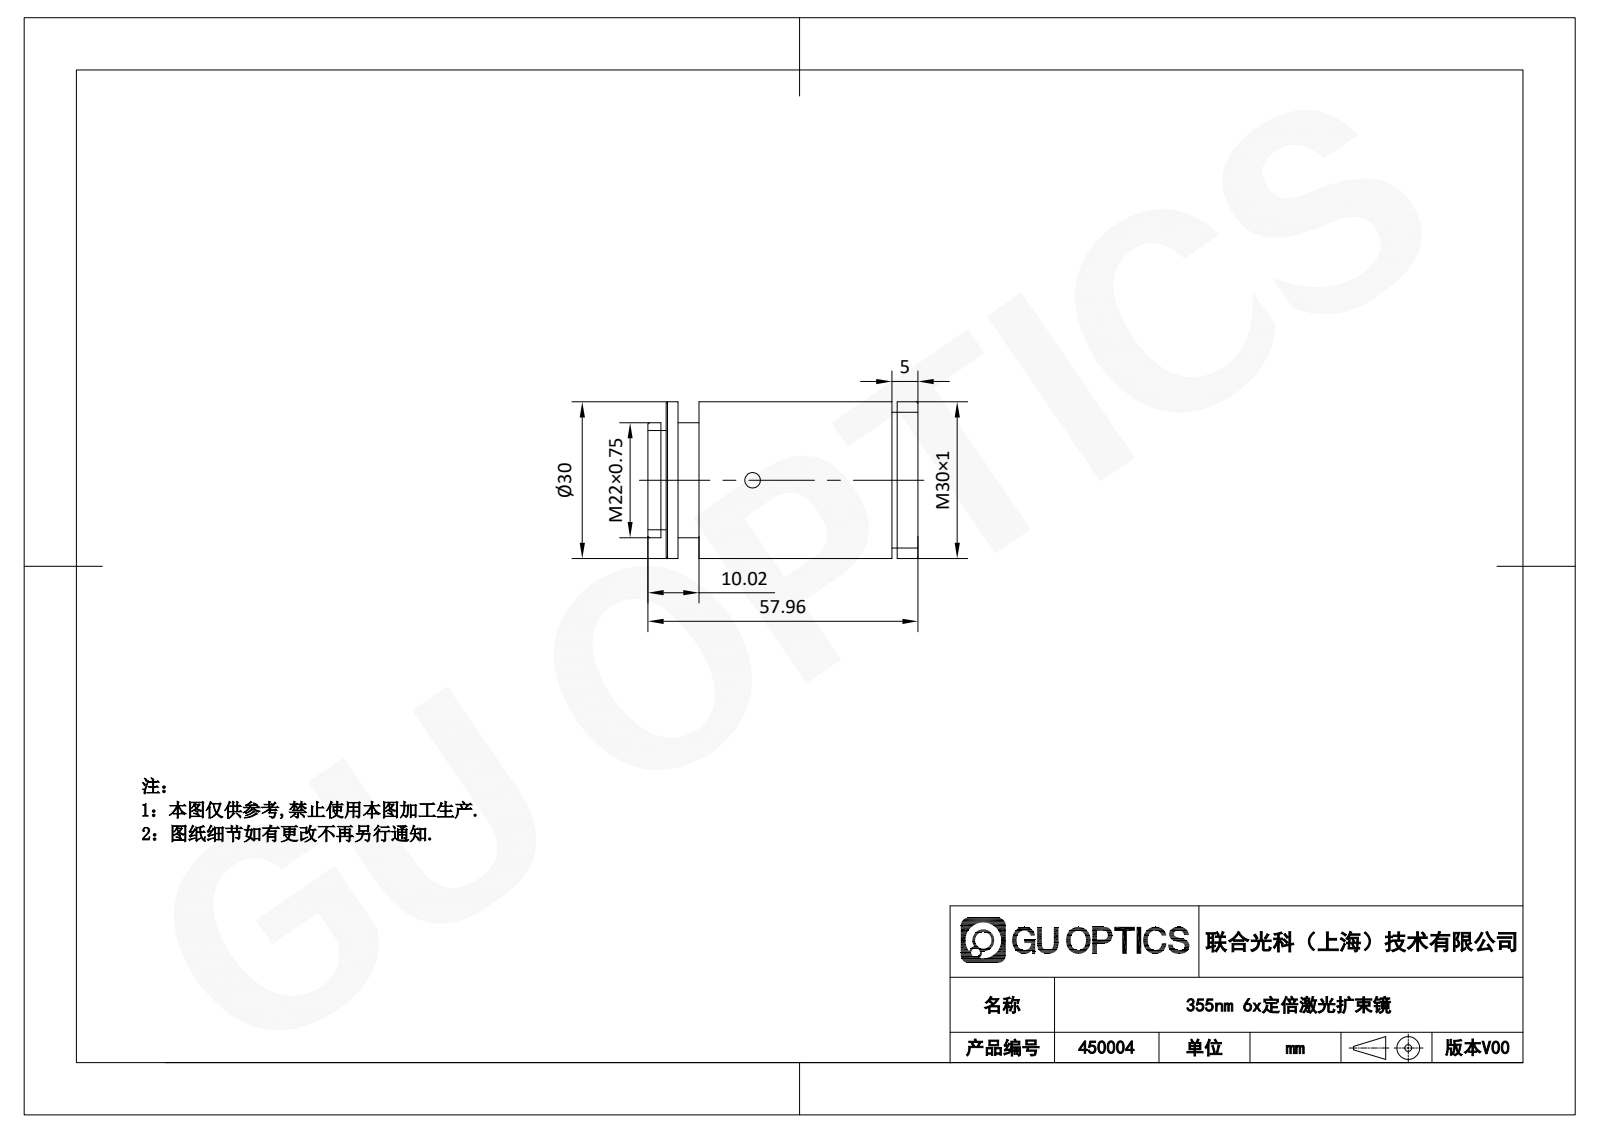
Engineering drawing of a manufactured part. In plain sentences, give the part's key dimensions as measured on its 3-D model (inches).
The part is named "450004". Its 3-D file was written by "SolidWorks 2020 (AUTOMOTIVE_DESIGN)". It is 1 solid with 43 faces: 11 planar, 22 cylindrical and 10 other. Overall it measures 2.282 by 1.181 by 1.181 inches. Its volume is 1.898 cubic inches and its surface area 16.19 square inches. Round holes: 1 of diameter 0.315, 1 of diameter 0.709. Round bosses or shafts: 1 of diameter 1.181, 1 of diameter 1.024, 1 of diameter 0.866, 1 of diameter 0.748. The main face-to-face distances are 0.157, 1.887, 1.987, 2.144, 0.099, 2.045, 0.257, 1.73, 0.138, 0.237.
